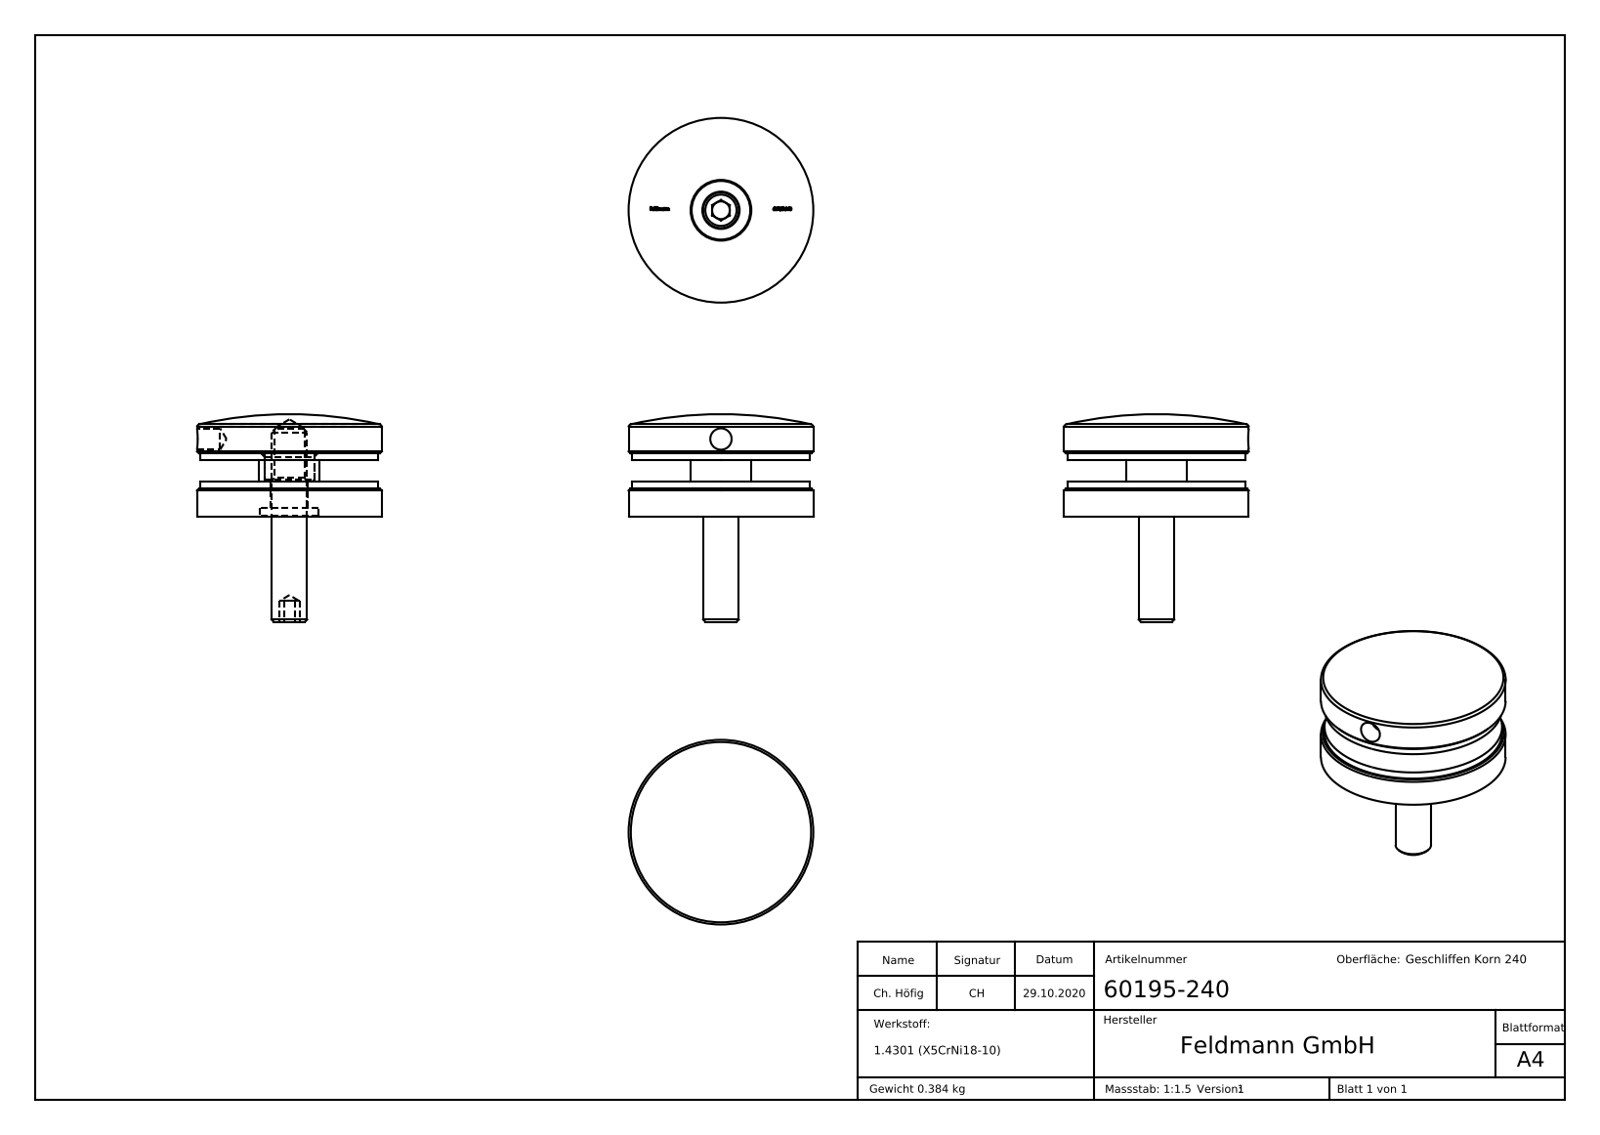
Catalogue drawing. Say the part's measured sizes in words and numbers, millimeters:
The part is named "60195-240; DIN913_DIN 913 M10x55; DIN913; 6019X-240 Konfig Teil3_6019X-XXX Teil3 (+7 more)". Its 3-D file was written by "SolidWorks 2018 (CONFIG_CONTROL_DESIGN)". It is 5 solids with 296 faces: 144 planar, 26 cylindrical and 126 other. Overall it measures 110 by 52 by 52 millimeters. Its volume is 48 144 cubic millimeters and its surface area 22 654 square millimeters. Round holes: 1 of diameter 6, 1 of diameter 8.5, 1 of diameter 10.5, 1 of diameter 14, 1 of diameter 16.5. Round bosses or shafts: 1 of diameter 52, 1 of diameter 50, 1 of diameter 17, 1 of diameter 10. The main face-to-face distances are 8, 10, 2, 18, 6, 16, 2.5, 5.5, 7.5, 13.5.
